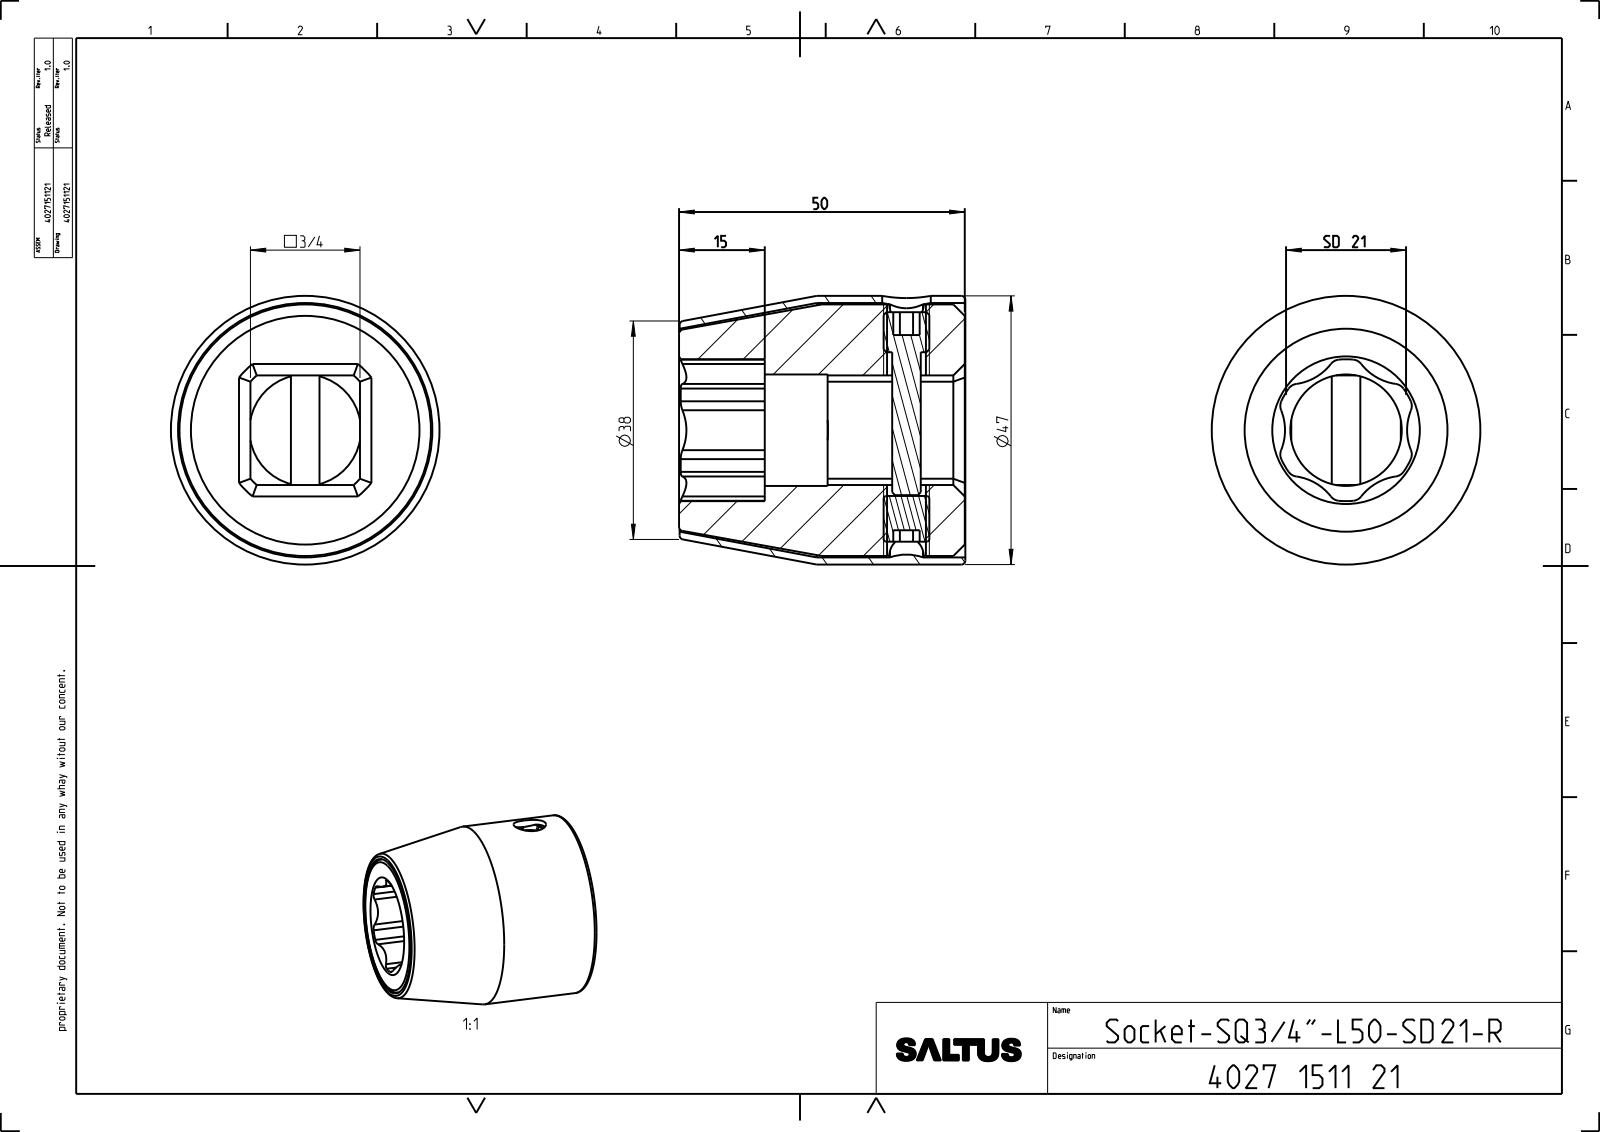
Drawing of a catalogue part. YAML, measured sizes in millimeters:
part_name: "4027911353; 4027036374; 0190131800_SPEC; 4027905697 (+1 more)"
step_written_by: "CREO PARAMETRIC BY PTC INC, 2022414 (CONFIG_CONTROL_DESIGN)"
units: millimeters
bodies: {solids: 4, faces: 129, planar: 36, cylindrical: 56, other: 37}
overall_size: [50.1, 47, 47]
volume: 57194
surface_area: 28010
round_holes:
  - {diameter: 6.8, count: 1}
  - {diameter: 8, count: 1}
  - {diameter: 8.5, count: 1}
  - {diameter: 19.5, count: 1}
  - {diameter: 44.5, count: 1}
round_bosses_or_shafts:
  - {diameter: 47, count: 1}
  - {diameter: 44, count: 1}
  - {diameter: 5, count: 1}
partial_cylinders:
  - {radius: 2, count: 12}
  - {radius: 9.3, count: 6}
  - {radius: 12.41, count: 1}
  - {radius: 12.8, count: 1}
face_to_face_distances: [19.18, 50, 35, 15, 35.1, 50.1, 49.9, 14.9, 24.1, 24]
